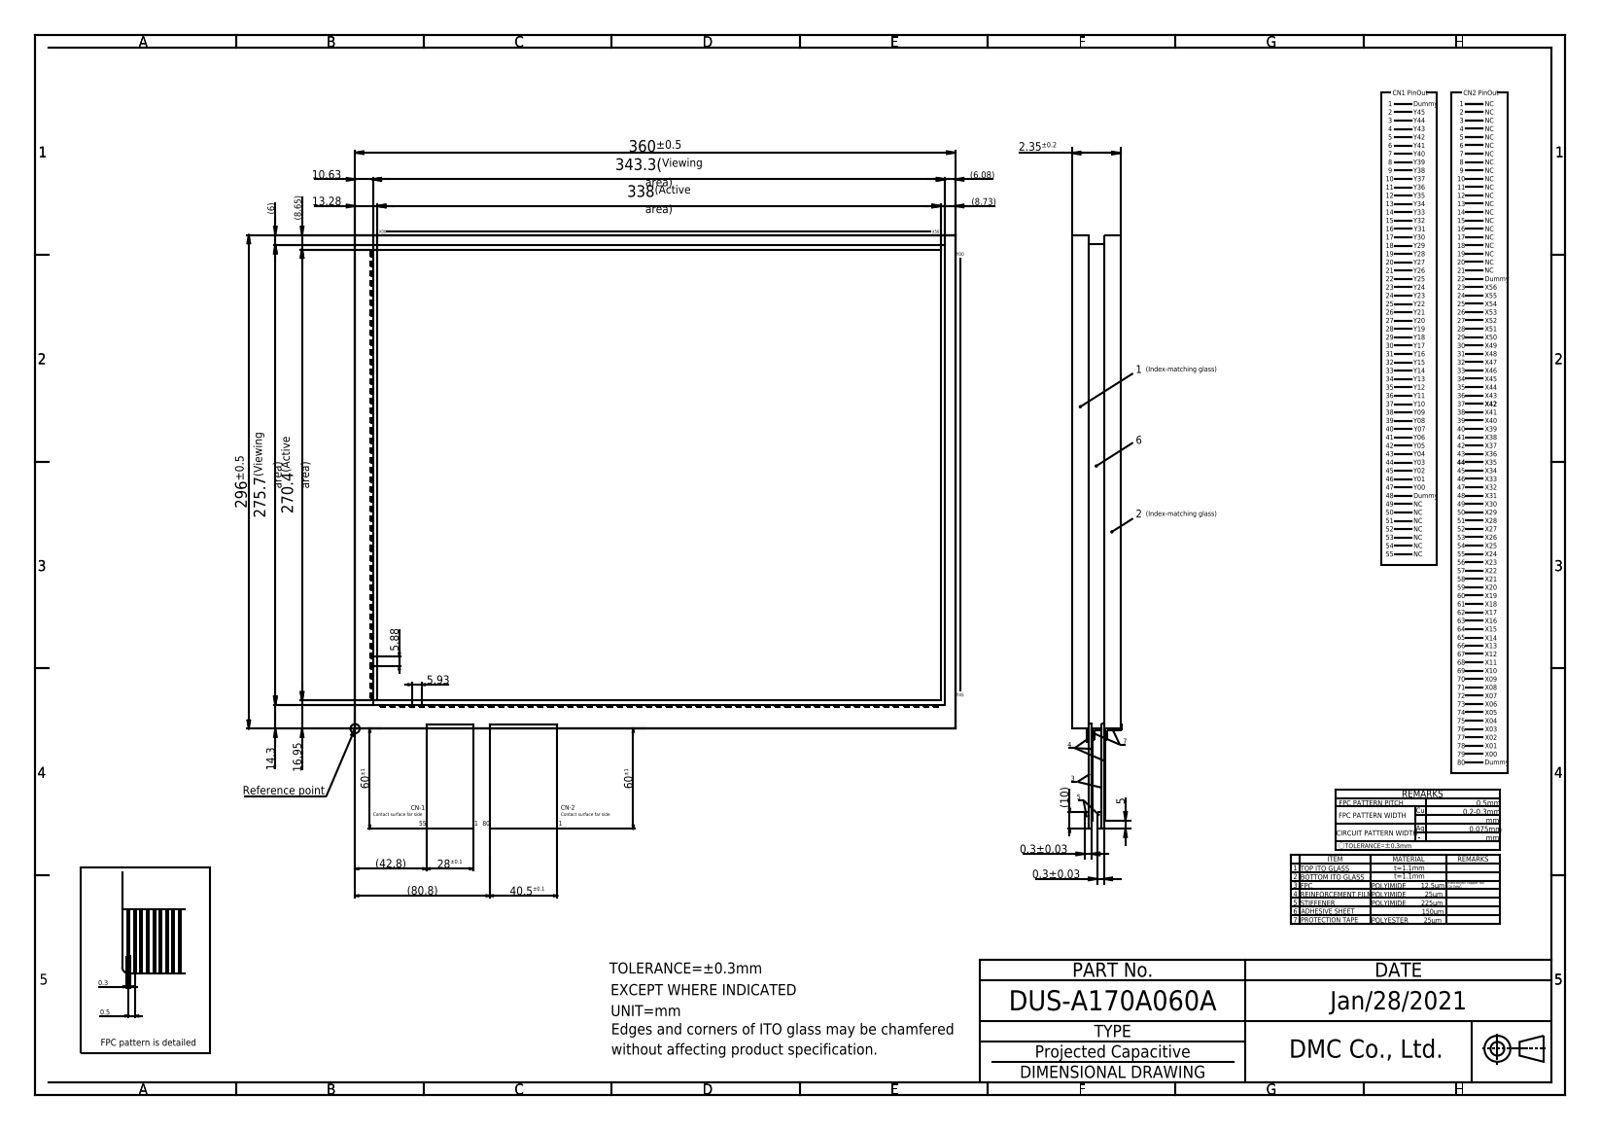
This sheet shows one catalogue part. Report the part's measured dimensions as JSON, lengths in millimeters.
{"part_name": "DUS-A170A060A", "step_written_by": "Autodesk Inventor 2020 (CONFIG_CONTROL_DESIGN)", "units": "millimeters", "bodies": {"solids": 1, "faces": 578, "planar": 574, "cylindrical": 4, "other": 0}, "overall_size": [504, 415.2, 2.35], "volume_mm3": 250672, "surface_area_mm2": 224757, "partial_cylinders_radius": [[0.2, 4]], "face_to_face_distances": [2.35, 1.1, 1.2, 1.15, 1.25, 1, 2.25, 296, 360, 0.8]}
